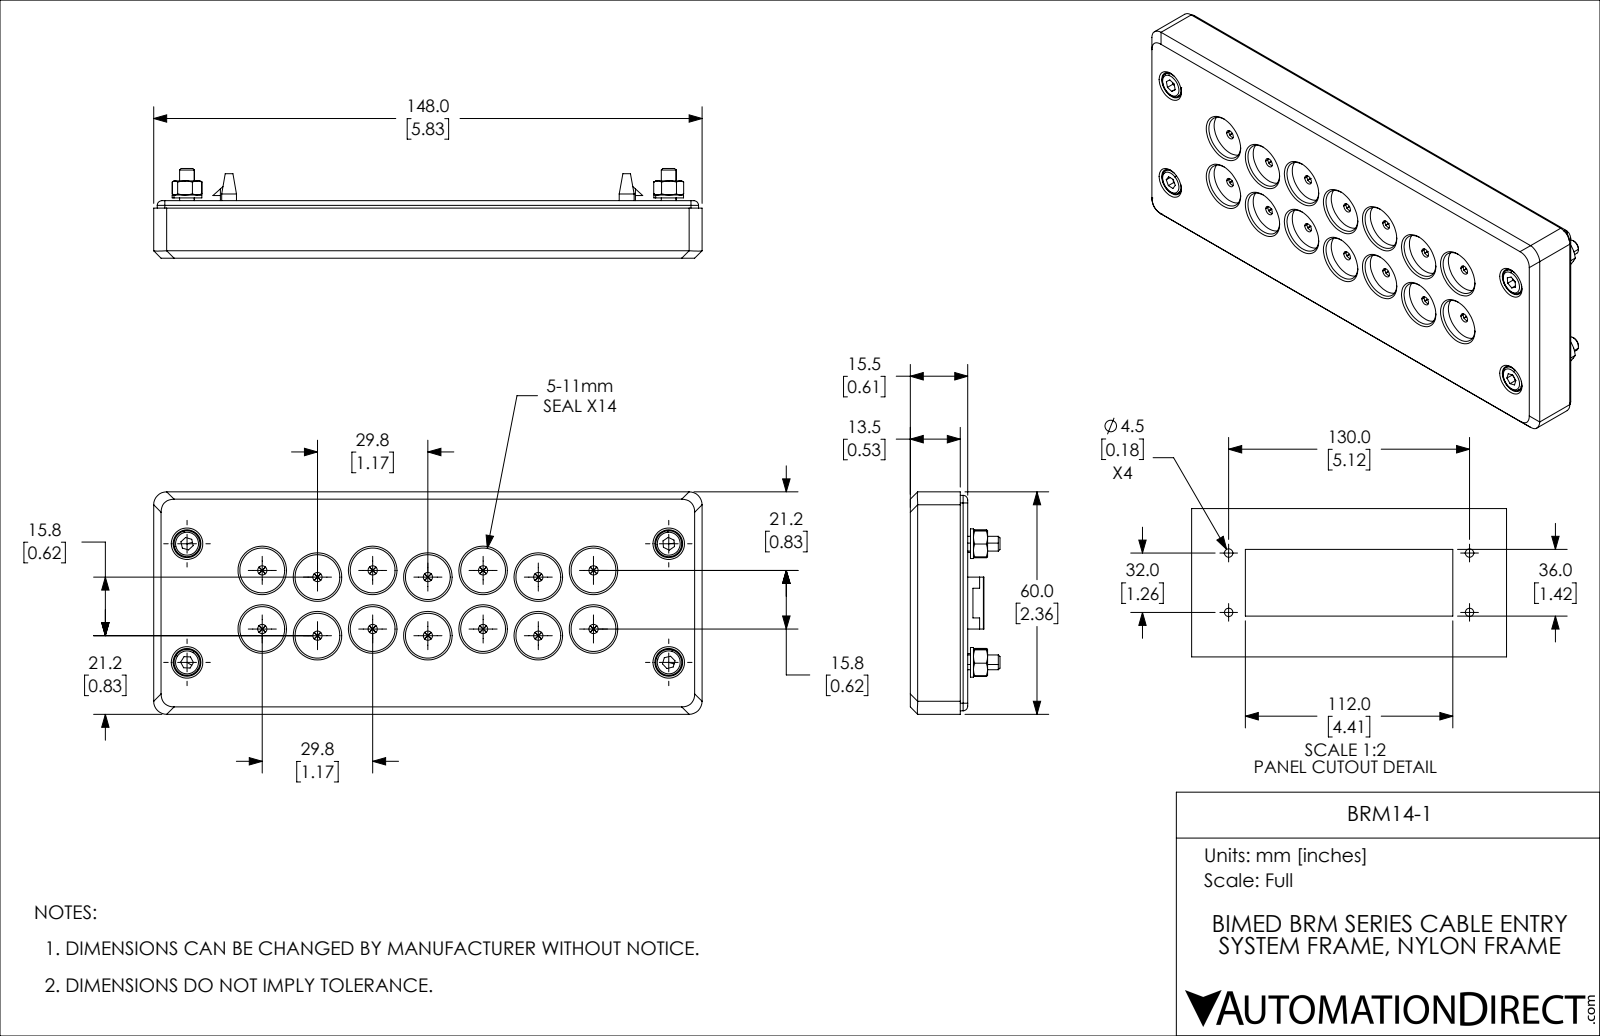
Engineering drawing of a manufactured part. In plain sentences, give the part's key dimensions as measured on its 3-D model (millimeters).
The part is named "BRM14-1". Its 3-D file was written by "SolidWorks 2021 (CONFIG_CONTROL_DESIGN)". It is 18 solids with 1231 faces: 385 planar, 574 cylindrical and 272 other. Overall it measures 148 by 60 by 24.2 millimeters. Its volume is 89 429 cubic millimeters and its surface area 89 519 square millimeters. Round holes: 21 of diameter 2.8, 18 of diameter 2.5, 14 of diameter 12.1, 14 of diameter 14, 4 of diameter 3.24, 4 of diameter 4.3, 4 of diameter 4.5, 4 of diameter 7.5. Round bosses or shafts: 16 of diameter 2.5, 8 of diameter 4, 4 of diameter 8, 4 of diameter 7. Partial cylindrical surfaces (rounded edges, fillets, slot ends): 28 of radius 1, 8 of radius 1.25, 8 of radius 5, 6 of radius 0.5, 4 of radius 2, 4 of radius 2.05, 4 of radius 3.5, 4 of radius 4.95. The main face-to-face distances are 0.8, 2, 2.8, 3, 5, 5.8, 2.5, 3.3, 8.3, 5.3. The hole center spacings are 15.01, 29.8, 33.73, 44.74, 15.8, 20.45, 23.06, 59.6.
